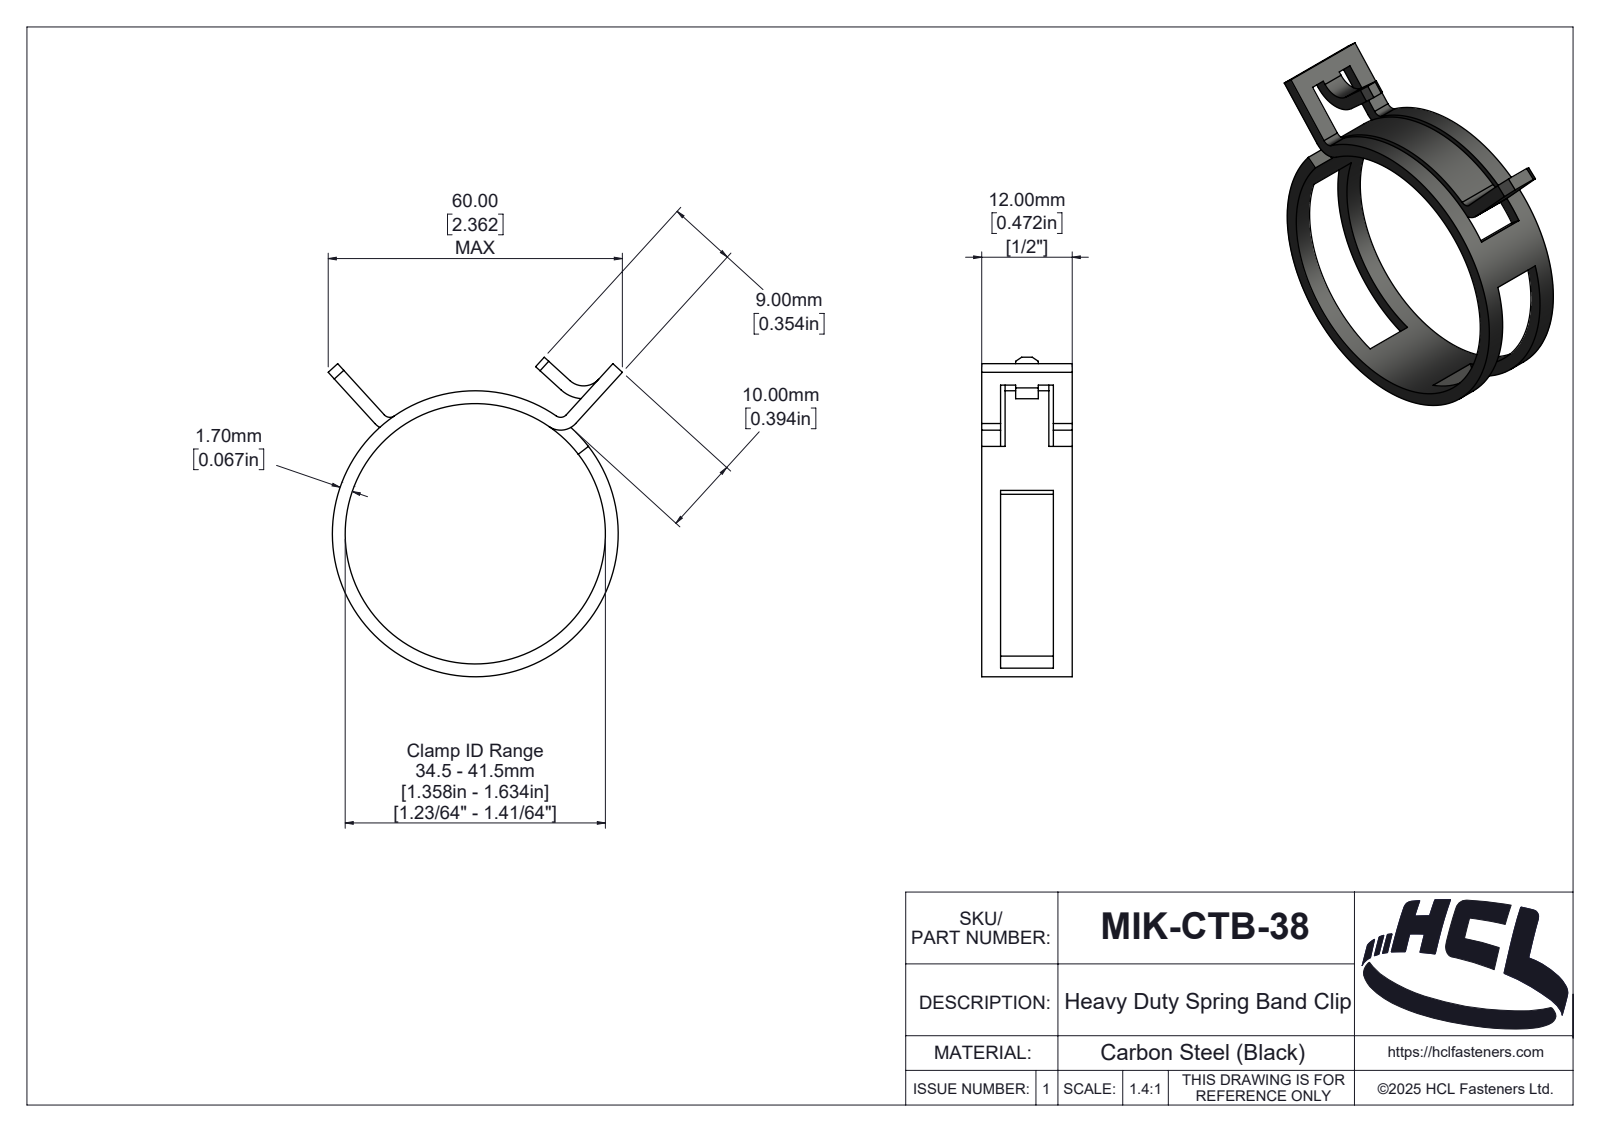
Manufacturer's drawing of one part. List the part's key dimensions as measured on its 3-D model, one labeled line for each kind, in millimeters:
Part name (STEP PRODUCT): MIK-CTB-38
STEP written by: SolidWorks 2025 (AUTOMOTIVE_DESIGN)
Units: millimetres
Bodies: 1 solid, 149 faces (36 planar, 64 cylindrical, 49 other)
Overall size (bounding box): 42.35 × 39 × 12
Volume: 1 785 mm³ · Surface area: 3 107 mm²
Round holes (diameter × count): ⌀34.5 ×1
Round bosses / shafts (diameter × count): ⌀37.9 ×1
Partial cylindrical surfaces — rounded edges, fillets, slot ends (radius × count): R2.7 ×3, R1 ×2, R0.33 ×1, R1.35 ×1, R1.68 ×1, R1.77 ×1, R2.14 ×1, R3.02 ×1
Main face-to-face distances: 2.5, 9.5, 12, 7, 3.1, 8.9, 0.6, 6.4, 1.7, 5.8
